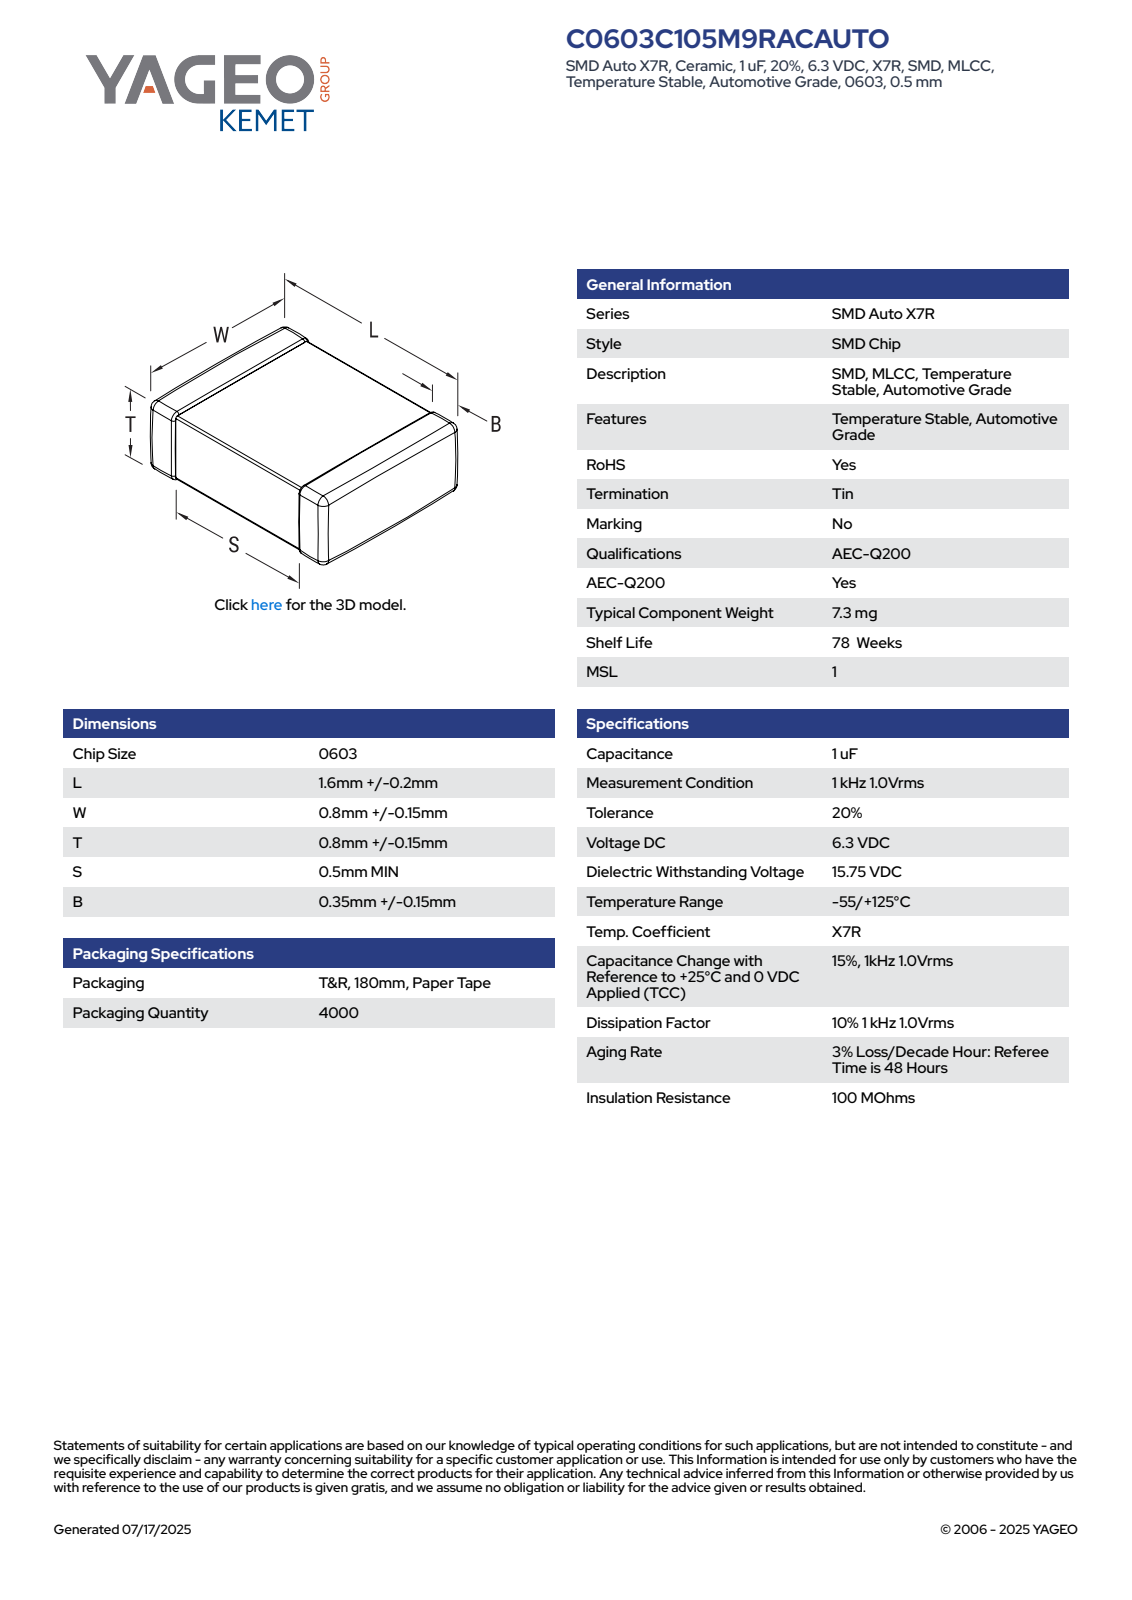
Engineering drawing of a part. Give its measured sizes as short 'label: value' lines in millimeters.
name: CCS_CCSTD_0603_L1.8W0.95T0.95B0.35
written by: SolidWorks 2021 (AUTOMOTIVE_DESIGN)
unit: mm
bodies: 4 solids, 121 faces (71 planar, 34 cylindrical, 16 other)
size: 1.8 × 0.95 × 0.95
volume: 2 mm³; area: 9 mm²
face distances: 0.93, 0.95, 0.91, 1.8, 0.92, 0.94, 0.83, 0.97, 0.38, 0.57
